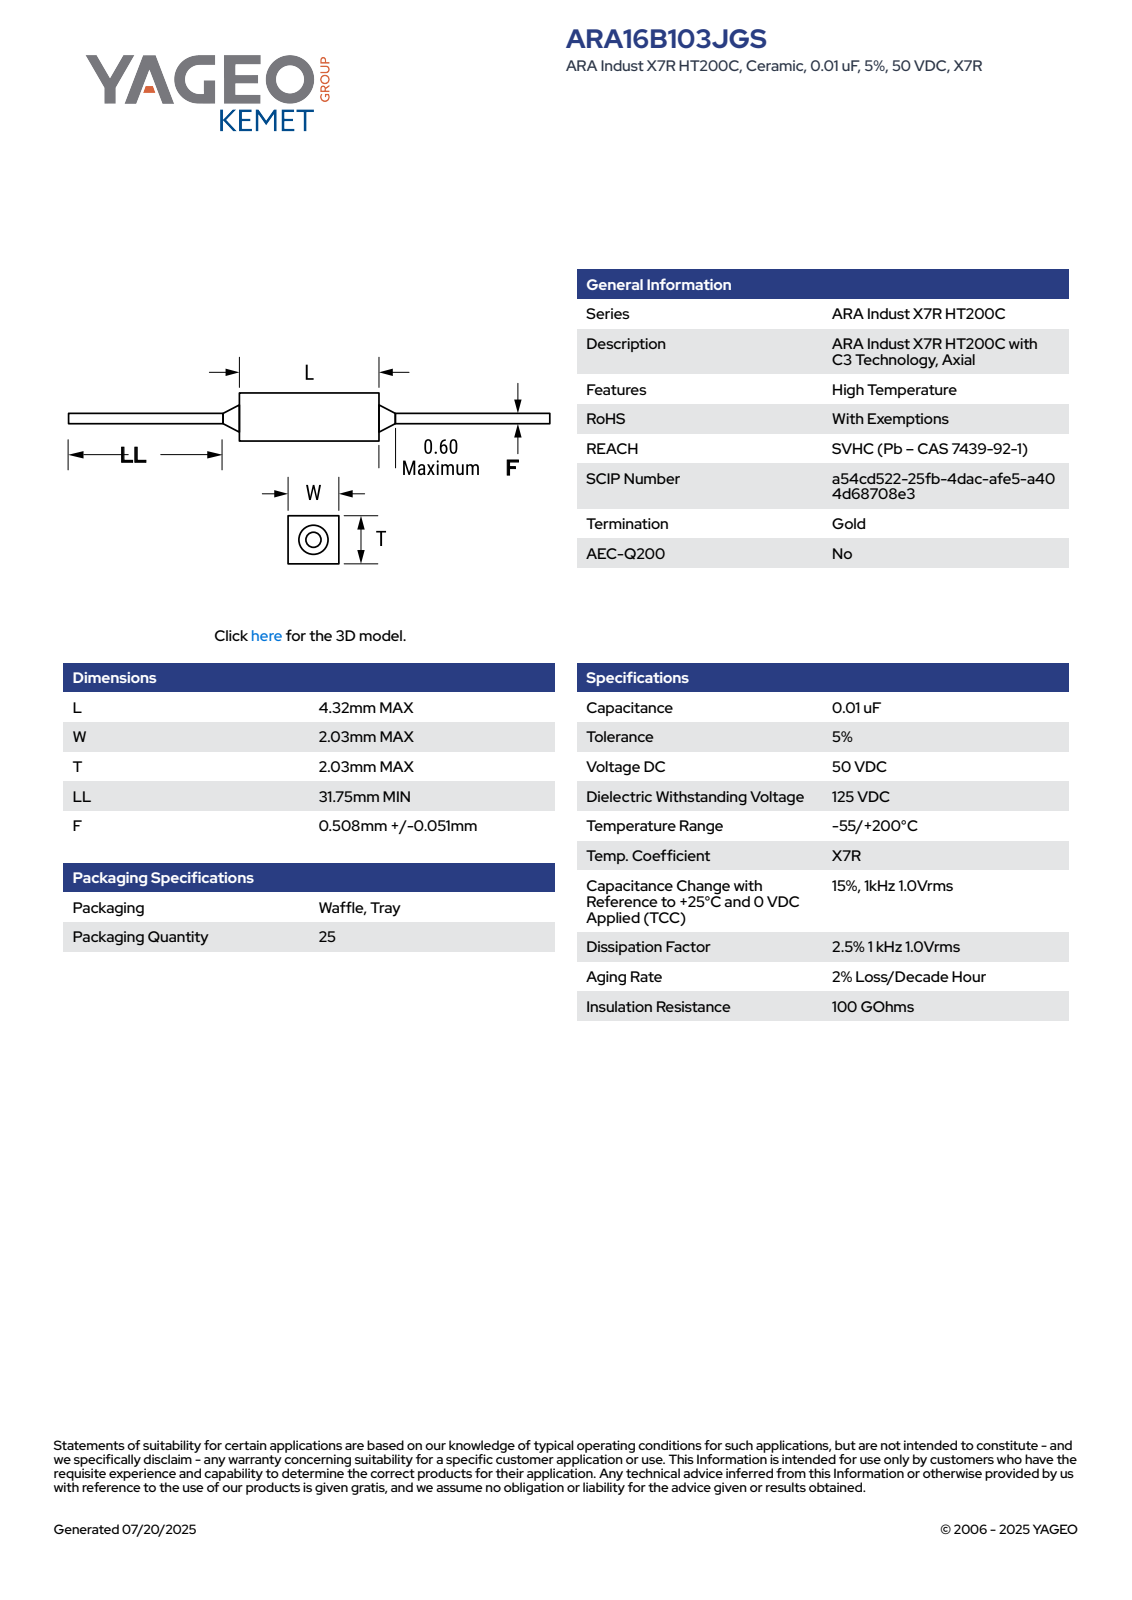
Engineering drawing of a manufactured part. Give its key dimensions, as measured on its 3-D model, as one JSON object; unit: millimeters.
{"part_name": "CCR_C3_16_L4.32T2.03LL3.175F0.559W2.03", "step_written_by": "SolidWorks 2021 (AUTOMOTIVE_DESIGN)", "units": "millimeters", "bodies": {"solids": 4, "faces": 73, "planar": 65, "cylindrical": 4, "other": 4}, "overall_size": [11.14, 2.04, 2.03], "volume_mm3": 20, "surface_area_mm2": 58, "round_bosses_or_shafts": [[0.56, 1]], "face_to_face_distances": [2.03, 2.04, 4.32, 3.41, 7.73, 11.14, 1.33, 0.71, 0.68, 1.39]}
